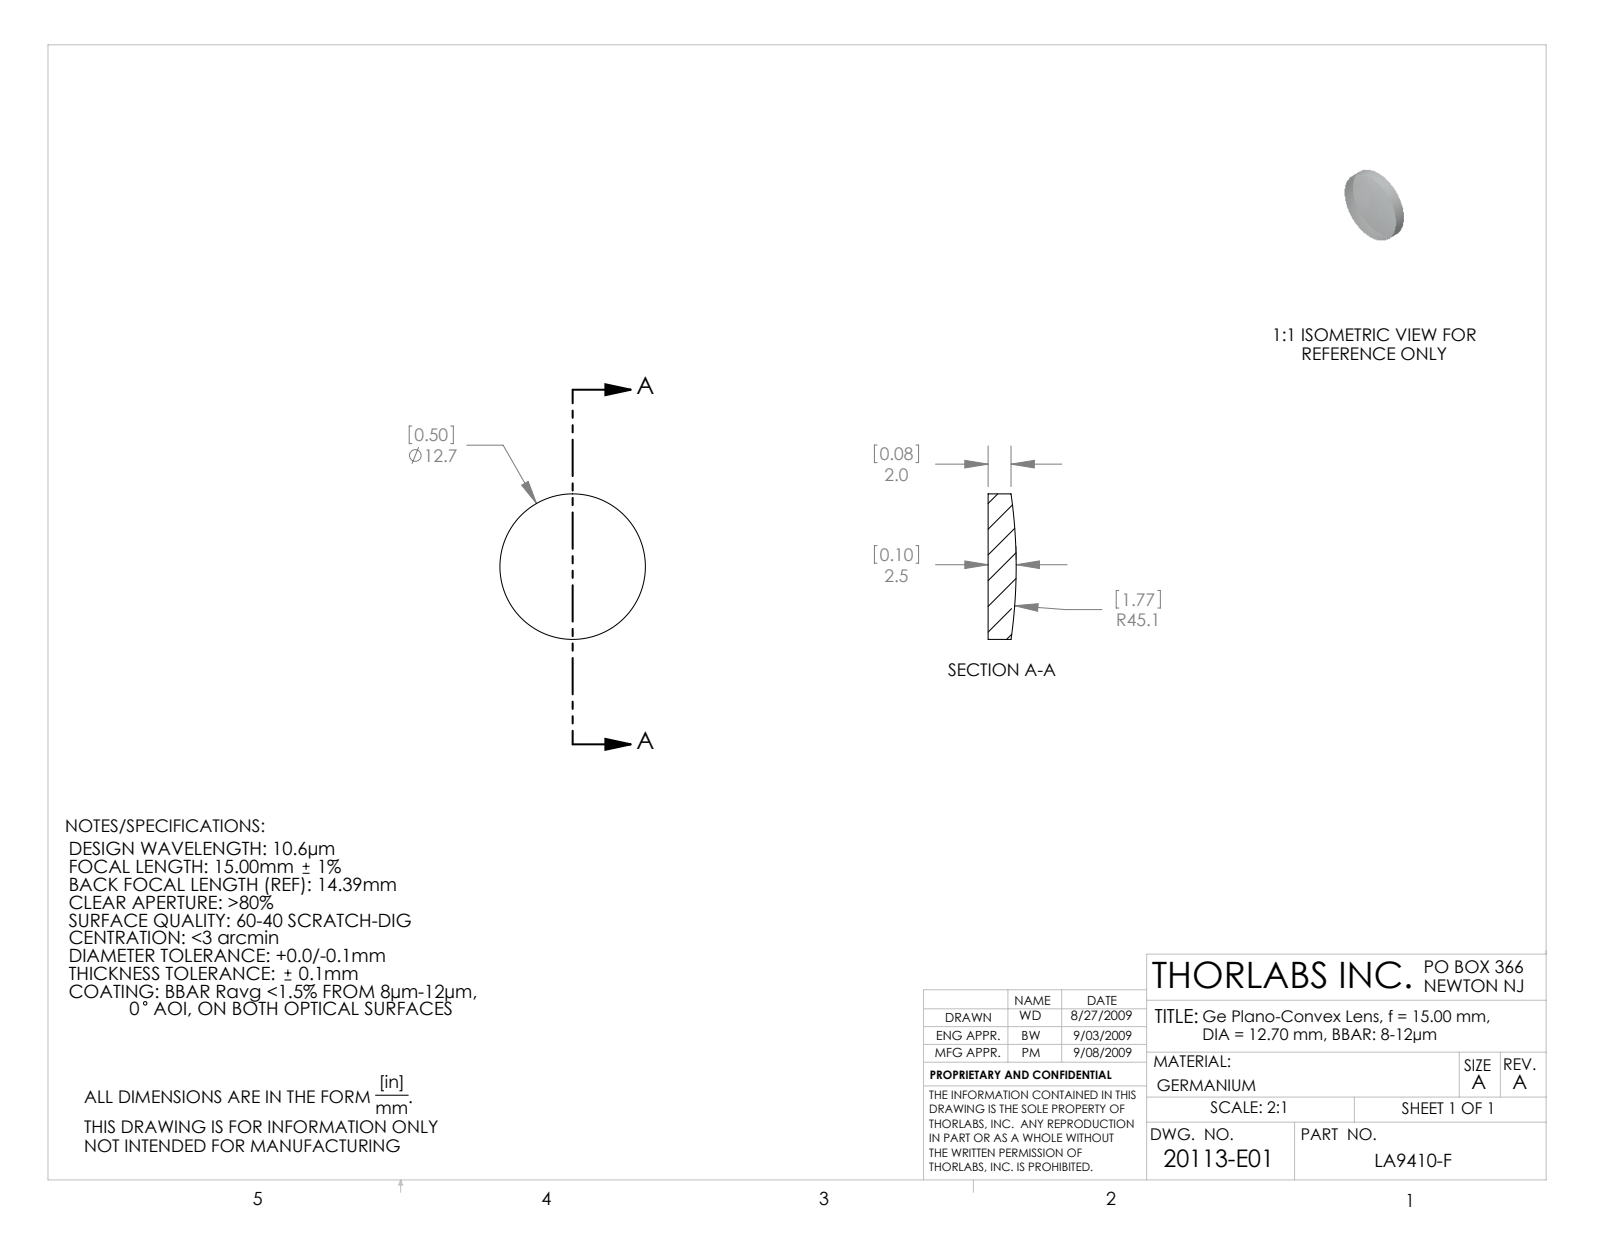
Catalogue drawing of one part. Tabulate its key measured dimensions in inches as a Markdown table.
| quantity | value |
| --- | --- |
| part name | 20113-E0W |
| STEP written by | SolidWorks 2007 (CONFIG_CONTROL_DESIGN) |
| units | inches |
| bodies | 1 solid, 5 faces (1 planar, 2 cylindrical, 2 other) |
| overall size | 0.5 × 0.5 × 0.096 |
| volume | 0.017 in³ |
| surface area | 0.518 in² |
| round bosses / shafts (diameter × count) | 0.5 × 1 |
